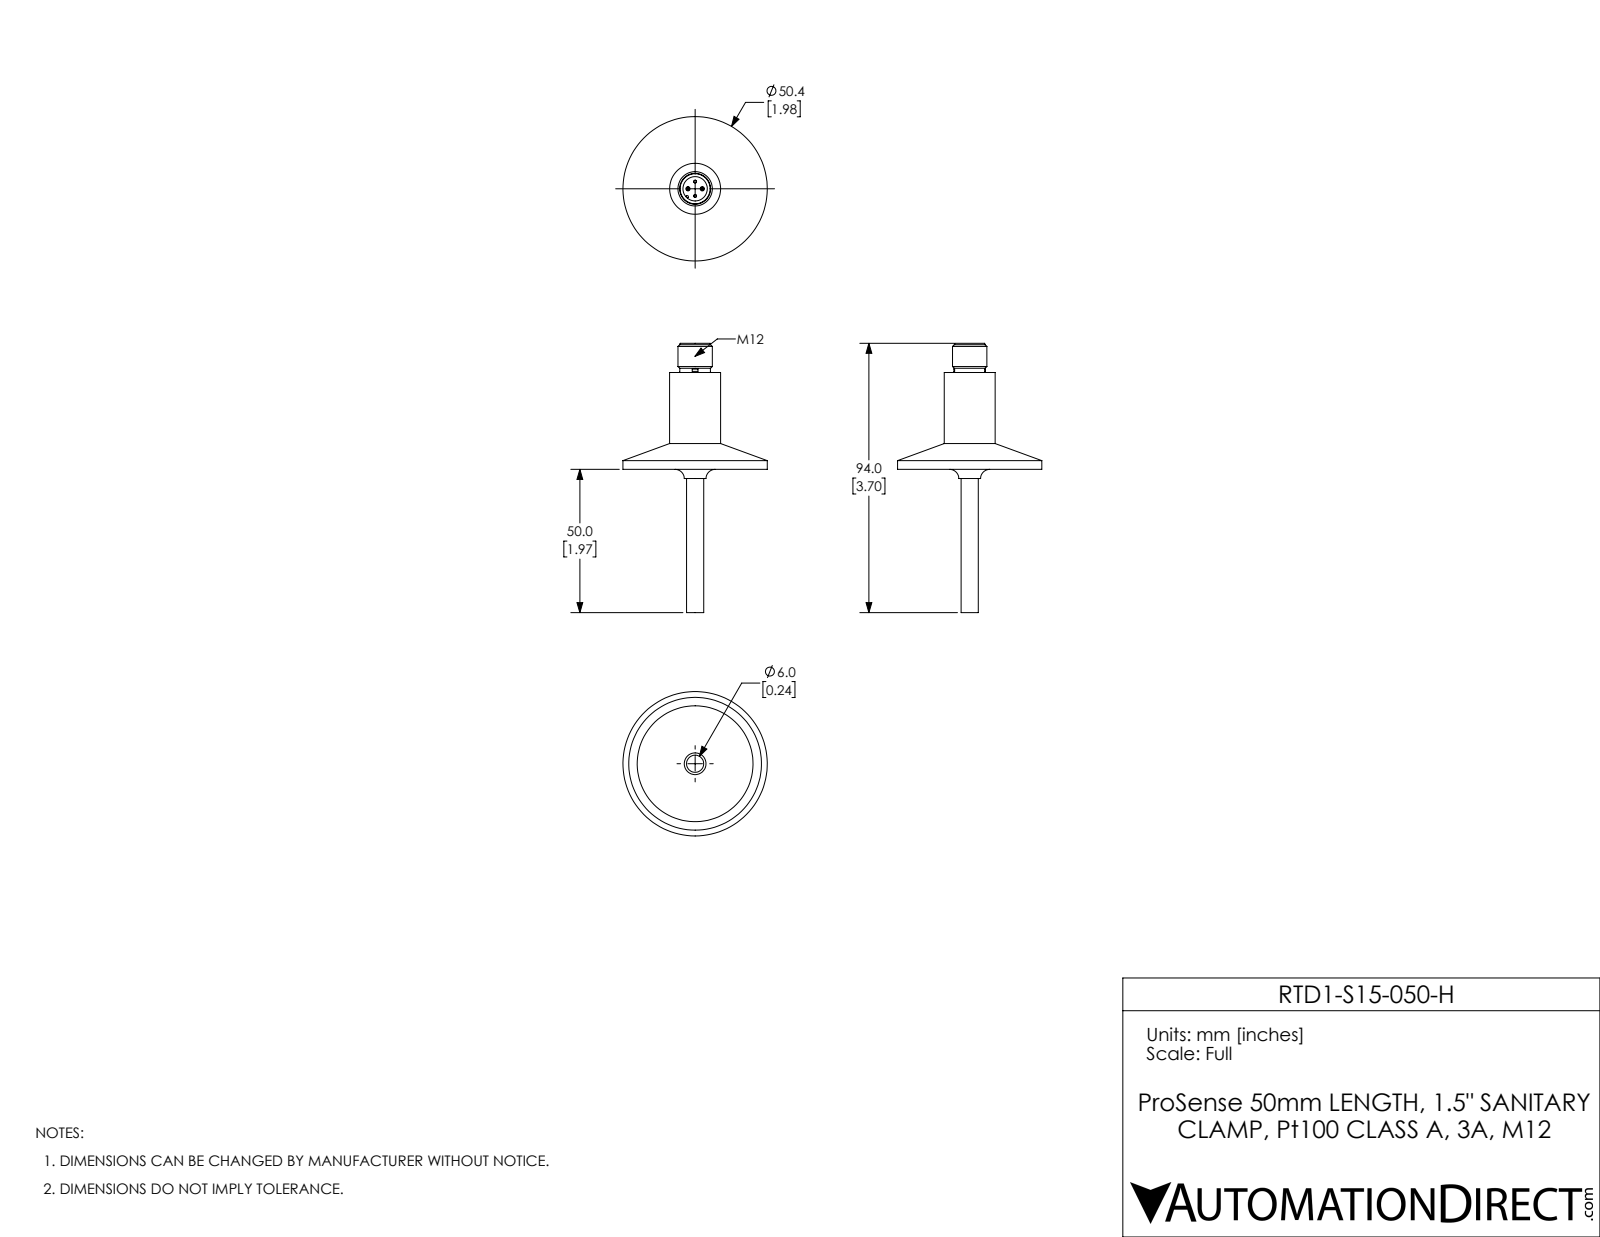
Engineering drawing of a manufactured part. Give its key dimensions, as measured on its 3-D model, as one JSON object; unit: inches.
{"part_name": "RTD1-S15-050-H", "step_written_by": "SolidWorks 2017 (AUTOMOTIVE_DESIGN)", "units": "inches", "bodies": {"solids": 1, "faces": 79, "planar": 26, "cylindrical": 23, "other": 30}, "overall_size": [3.701, 1.984, 1.984], "volume_in3": 1.208, "surface_area_in2": 12.13, "round_holes": [[0.335, 1]], "round_bosses_or_shafts": [[0.04, 4], [1.984, 1], [0.701, 1], [0.472, 1], [0.421, 1], [0.413, 1], [0.236, 1]], "partial_cylinders_radius": [[0.016, 1]], "face_to_face_distances": [1.331, 1.378, 0.047, 1.732, 0.402, 0.354, 1.969, 3.299, 3.346, 3.701]}
